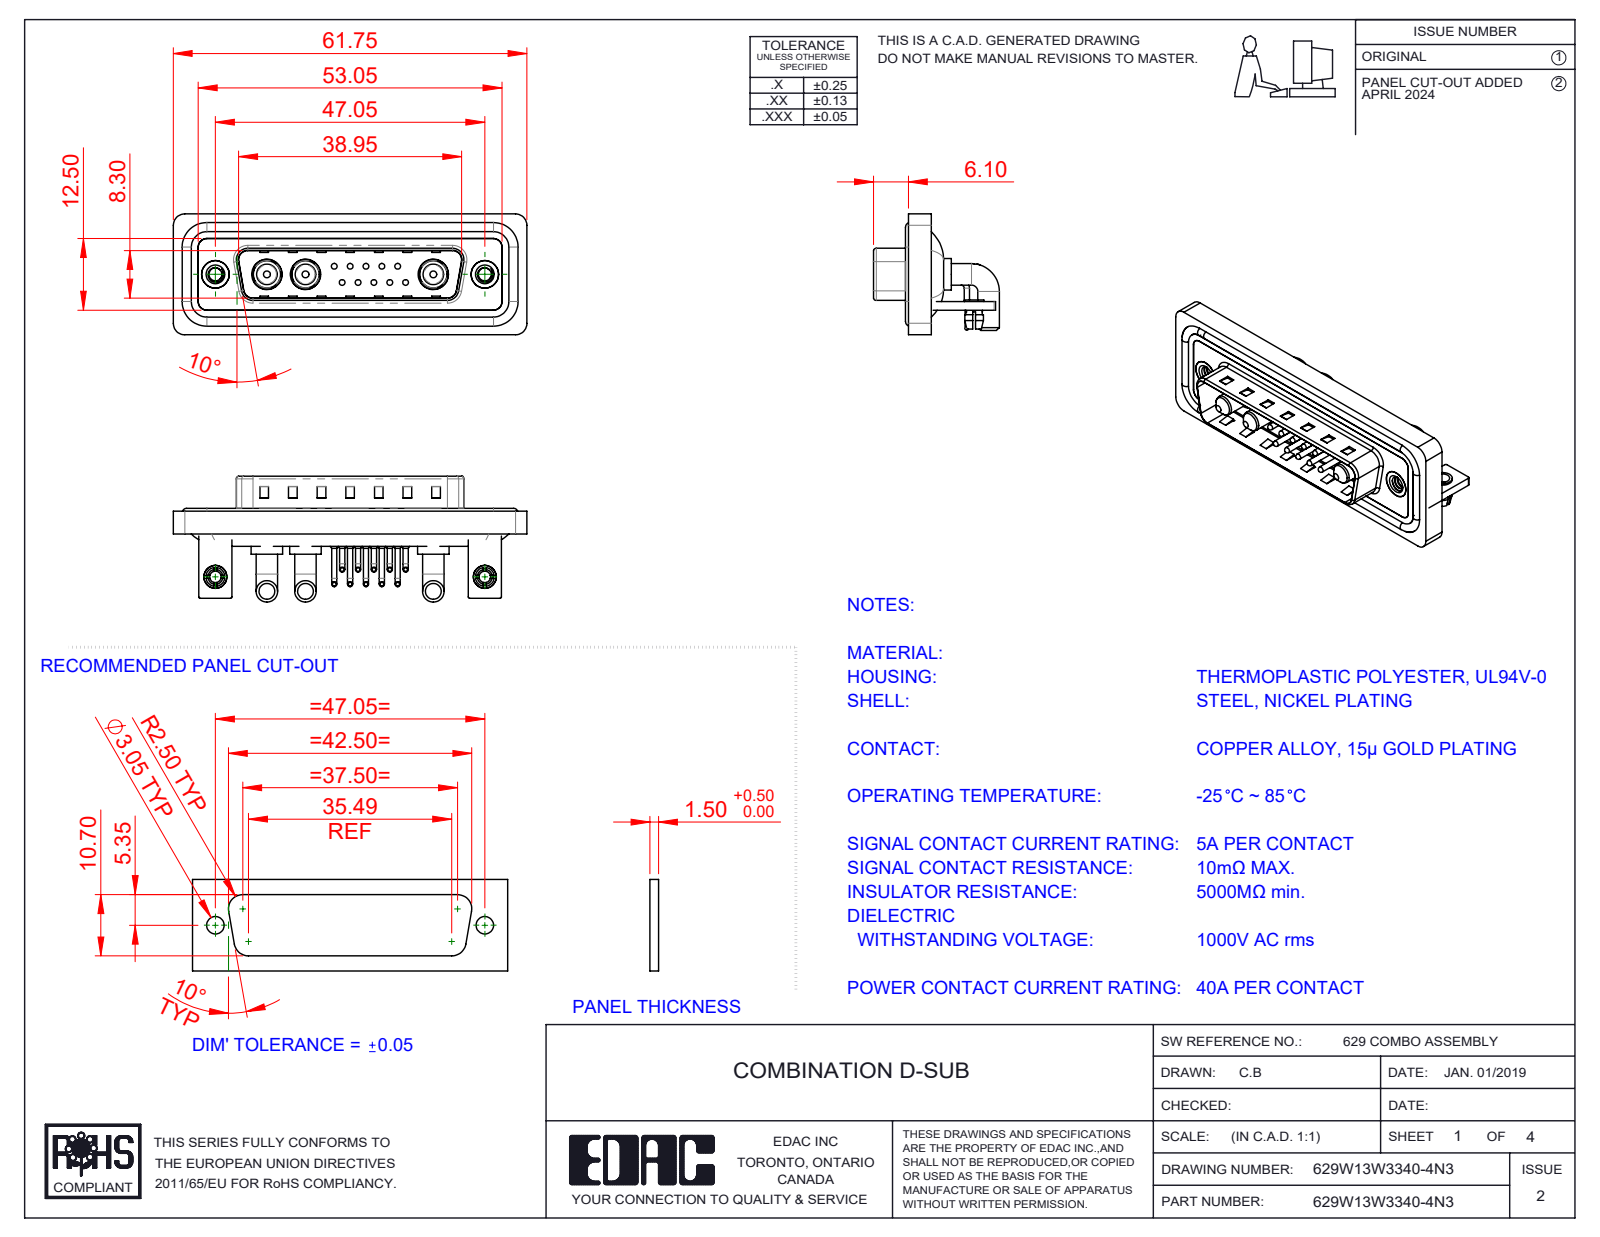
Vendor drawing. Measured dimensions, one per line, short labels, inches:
name: 629Combo Contact Row 1; 629Combo Housing_13W3; 629Combo Waterproof Housing_25 Contacts; Power Pin_40A RA (+7 more)
written by: SolidWorks 2023 (CONFIG_CONTROL_DESIGN)
unit: in
bodies: 27 solids, 1844 faces (947 planar, 661 cylindrical, 236 other)
size: 2.431 × 0.865 × 0.831
volume: 0.497 in³; area: 20.81 in²
holes: 12× ⌀0.079, 10× ⌀0.03, 10× ⌀0.063, 3× ⌀0.191, 3× ⌀0.209, 2× ⌀0.089, 2× ⌀0.098, 2× ⌀0.126, 2× ⌀0.157, 2× ⌀0.189, 2× ⌀0.197
bosses: 20× ⌀0.035, 10× ⌀0.059, 10× ⌀0.039, 10× ⌀0.026, 6× ⌀0.148, 4× ⌀0.063, 3× ⌀0.217, 3× ⌀0.205
rounds: 19× R0.079, 18× R0.059, 16× R0.01, 10× R0.04, 9× R0.02, 8× R0.063, 4× R0.024, 4× R0.026
face distances: 0.016, 0.031, 0.059, 0.114, 0.083, 0.043, 0.161, 0.063, 0.146, 0.177
hole spacings: 0.124, 0.109, 0.198, 0.218, 0.295, 0.198, 0.327, 0.398
